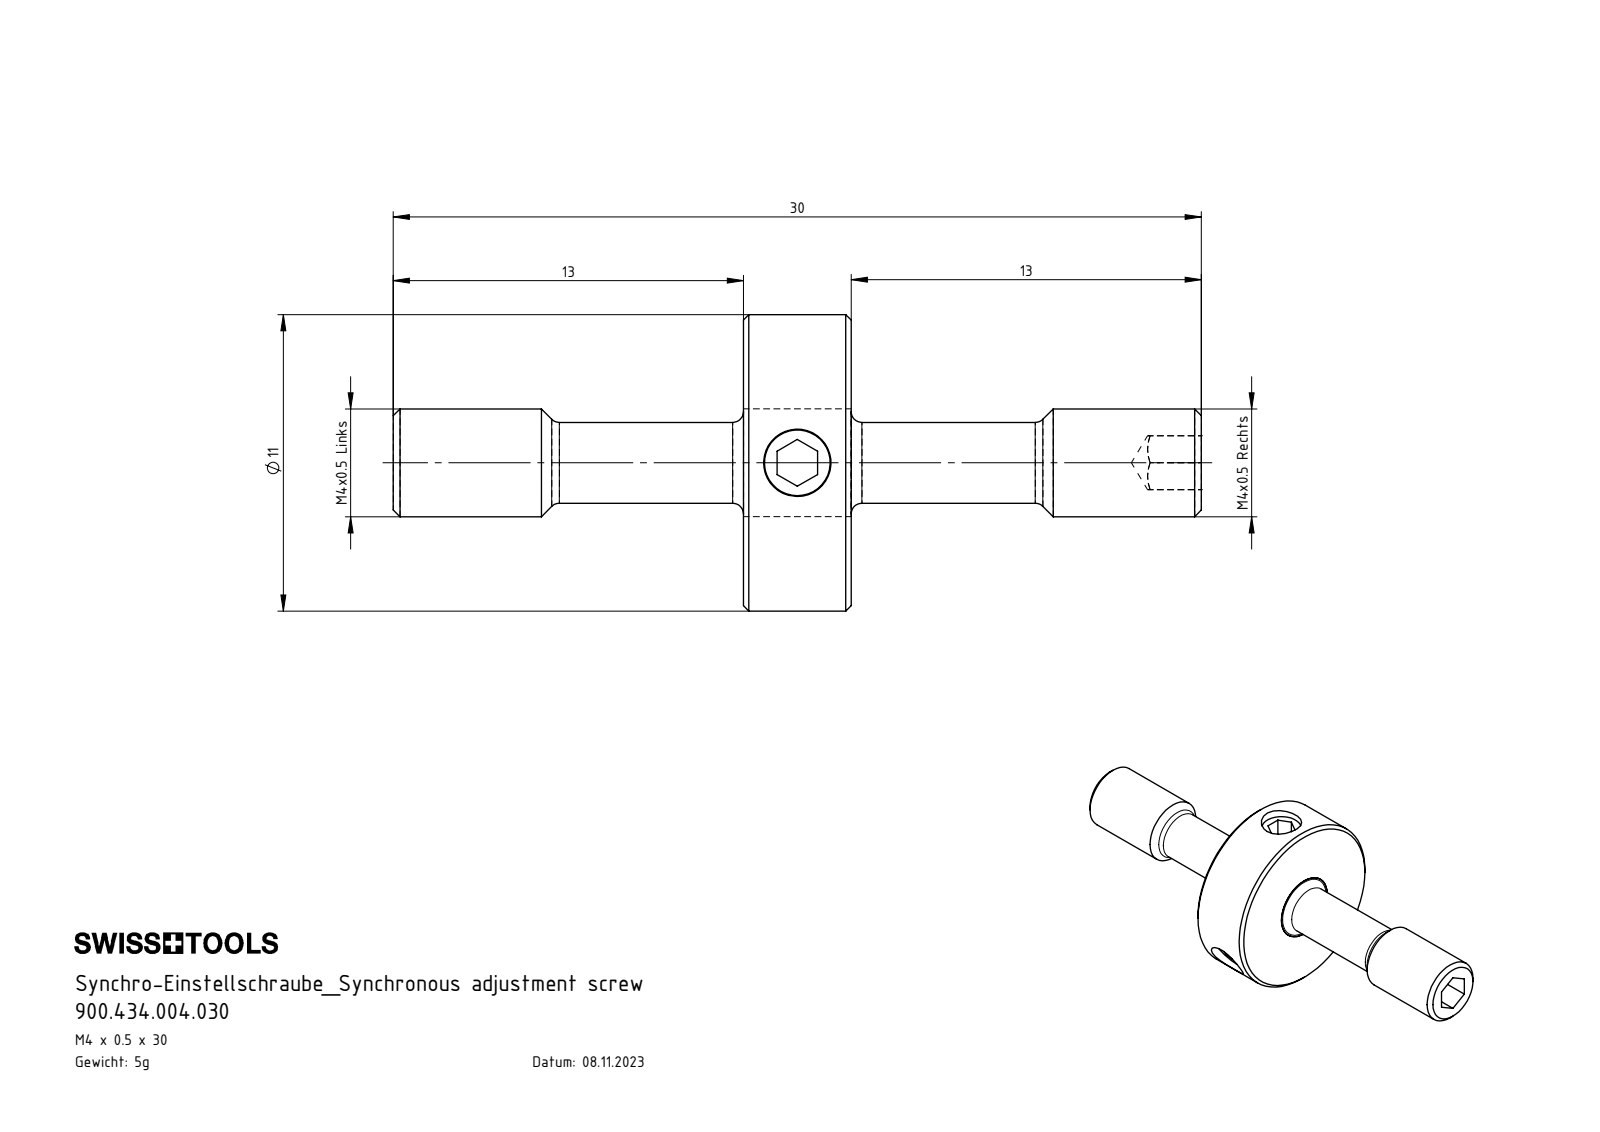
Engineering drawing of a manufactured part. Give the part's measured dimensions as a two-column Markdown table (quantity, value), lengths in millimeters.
| quantity | value |
| --- | --- |
| part name | 900.434.004.030; Z25-ER3.002.004_A; ISO 4026 - M3 x 3; Z32-ER3.001.030_A |
| STEP written by | SolidWorks 2022 (AUTOMOTIVE_DESIGN) |
| units | millimeters |
| bodies | 5 solids, 99 faces (39 planar, 26 cylindrical, 34 other) |
| overall size | 30 × 11 × 11 |
| volume | 614 mm³ |
| surface area | 925 mm² |
| round holes (diameter × count) | 2.5 × 3 |
| round bosses / shafts (diameter × count) | 3 × 4, 11 × 1, 4 × 1 |
| main face-to-face distances | 4, 13, 17, 1.5, 2, 14.25, 15.75, 1.25, 2.75, 3 |
